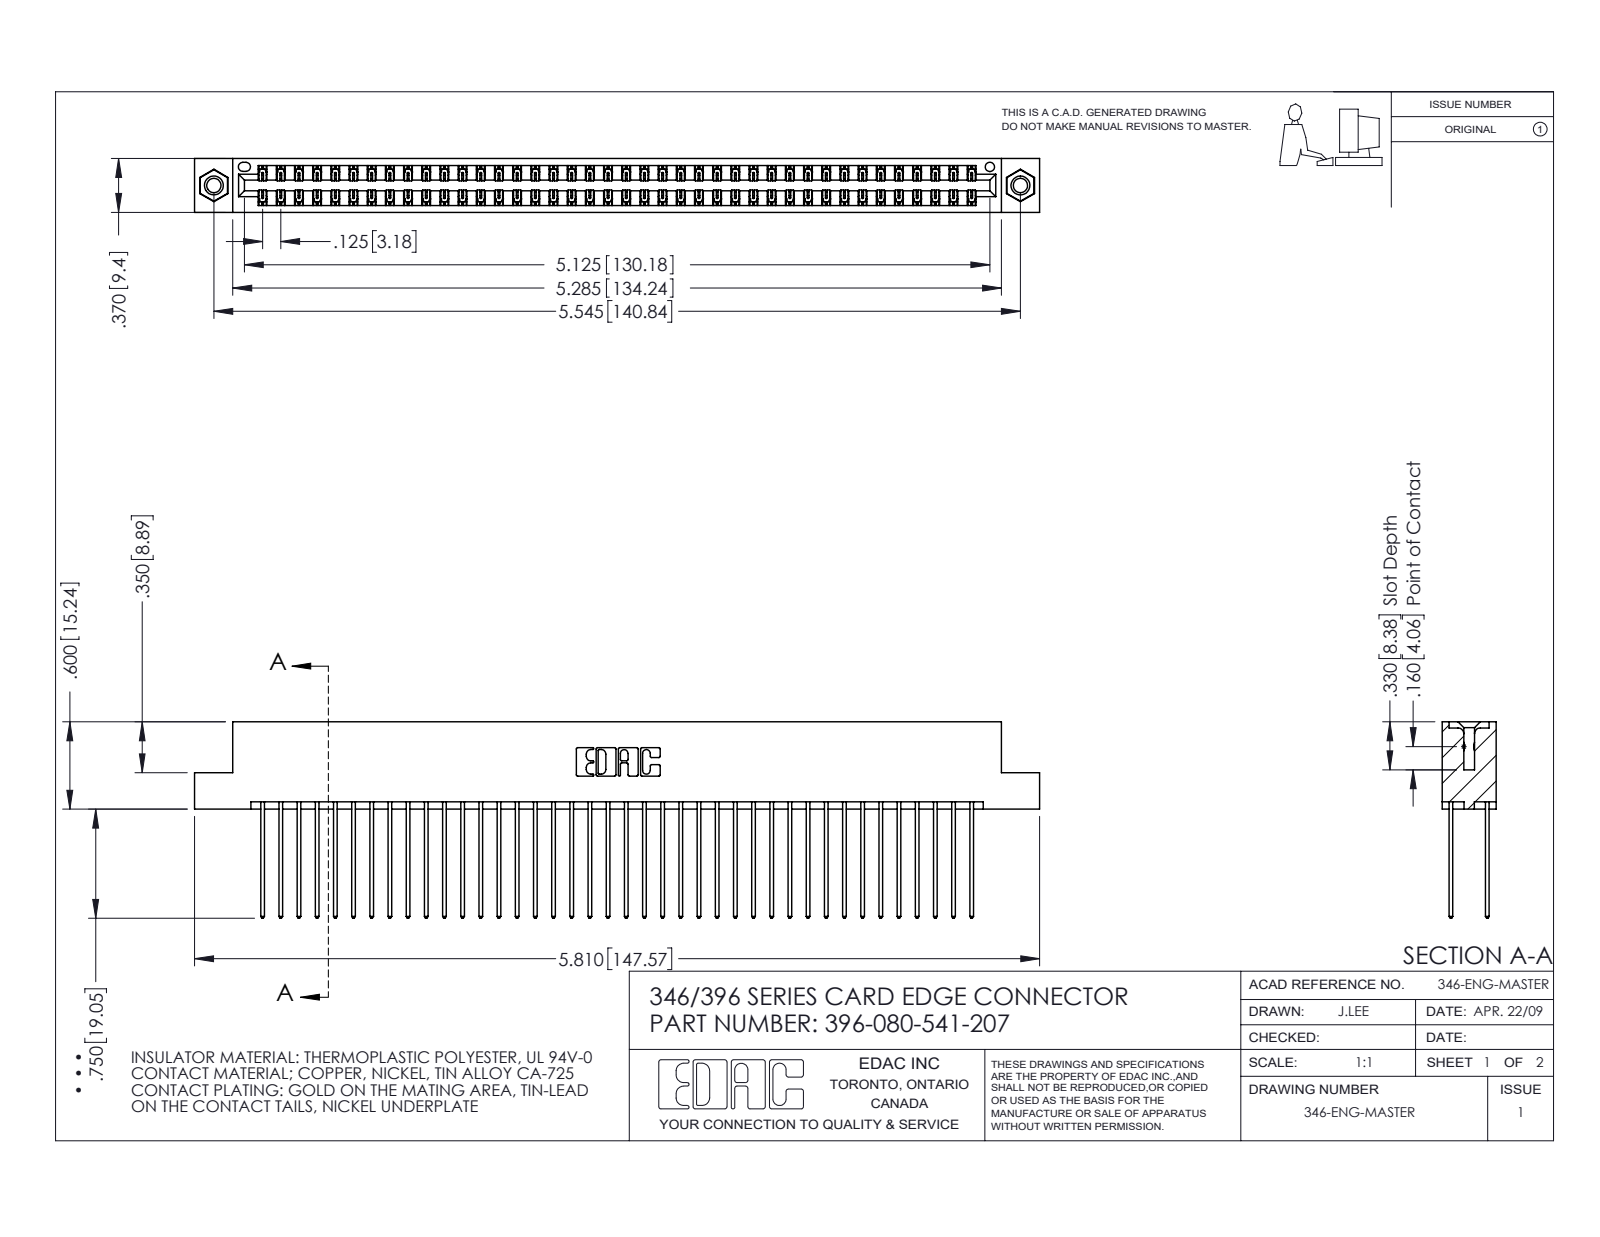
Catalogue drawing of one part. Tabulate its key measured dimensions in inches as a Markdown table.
| quantity | value |
| --- | --- |
| part name | 396-080-541-207; 345-250-001_345-250-005-103; 345-292-001_345-293-141; 346 Part_Flush Mounting Lugs - 0.156 Dia-TI |
| STEP written by | SolidWorks 2016 (CONFIG_CONTROL_DESIGN) |
| units | inches |
| bodies | 83 solids, 4342 faces (2908 planar, 1418 cylindrical, 16 other) |
| overall size | 5.81 × 1.35 × 0.37 |
| volume | 0.904 in³ |
| surface area | 34.99 in² |
| round holes (diameter × count) | 0.098 × 2, 0.125 × 2, 0.156 × 2, 0.064 × 1 |
| round bosses / shafts (diameter × count) | 0.155 × 2 |
| partial cylindrical surfaces (radius × count) | 0.006 × 120, 0.01 × 80, 0.01 × 22, 0.007 × 6, 0.031 × 6, 0.026 × 3, 0.014 × 2, 0.022 × 2 |
| main face-to-face distances | 0.048, 0.322, 0.25, 0.072, 0.298, 0.025, 0.37, 0.275, 0.225, 0.148 |
| hole center spacings | 0.246, 5.336, 5.545 |
